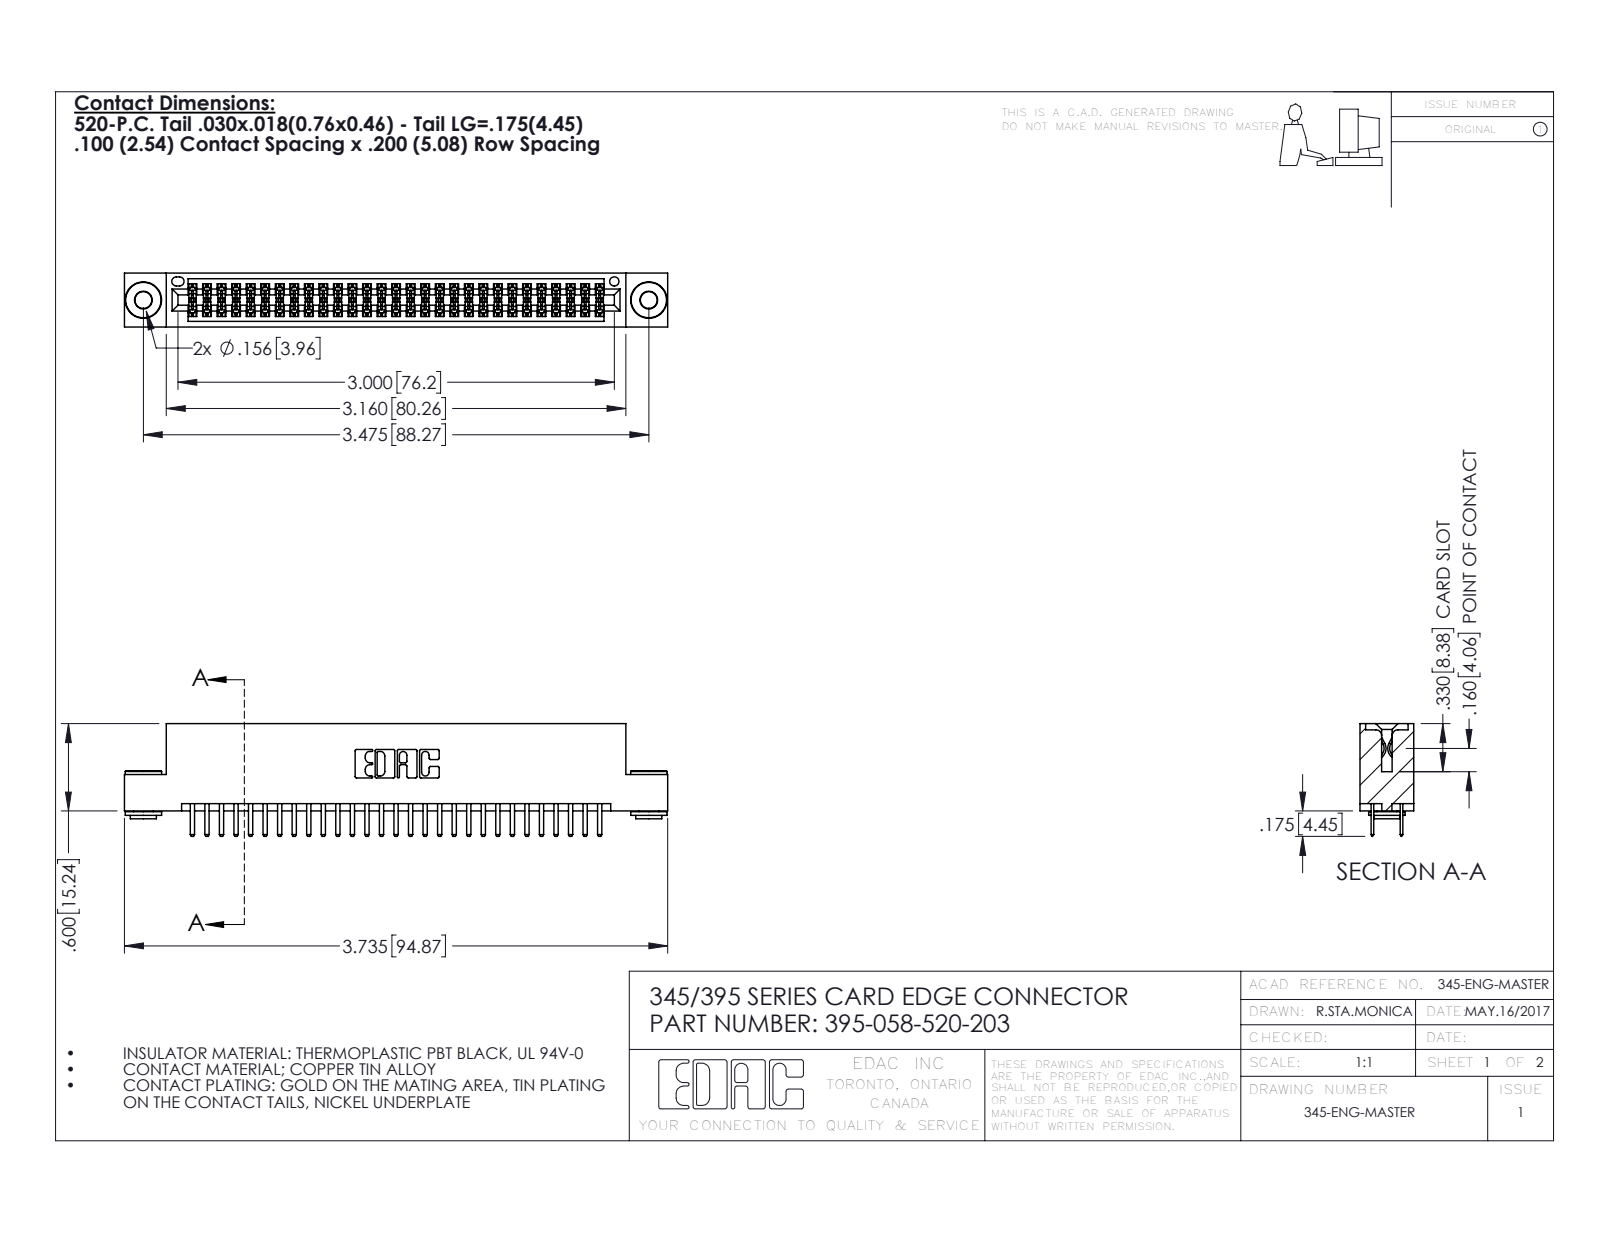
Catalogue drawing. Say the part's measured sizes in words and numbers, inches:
The part is named "345 Part_Flush Mounting Lugs - 0.156 Dia-TH; 395-058-520-203; 345-250-002_345-250-002-102; 345-292-001_345-293-120". Its 3-D file was written by "SolidWorks 2016 (CONFIG_CONTROL_DESIGN)". It is 61 solids with 3296 faces: 2120 planar, 1168 cylindrical and 8 other. Overall it measures 3.735 by 0.775 by 0.37 inches. Its volume is 0.555 cubic inches and its surface area 20.67 square inches. Round holes: 2 of diameter 0.116, 2 of diameter 0.156, 1 of diameter 0.064. Round bosses or shafts: 2 of diameter 0.25, 2 of diameter 0.18, 2 of diameter 0.136. Partial cylindrical surfaces (rounded edges, fillets, slot ends): 87 of radius 0.006, 62 of radius 0.01, 22 of radius 0.01, 6 of radius 0.007, 6 of radius 0.031, 3 of radius 0.026, 2 of radius 0.014, 2 of radius 0.019. The main face-to-face distances are 0.072, 0.298, 0.2, 0.37, 0.025, 0.098, 0.272, 0.225, 0.022, 0.072. The hole center spacings are 0.27, 3.24, 3.475.
